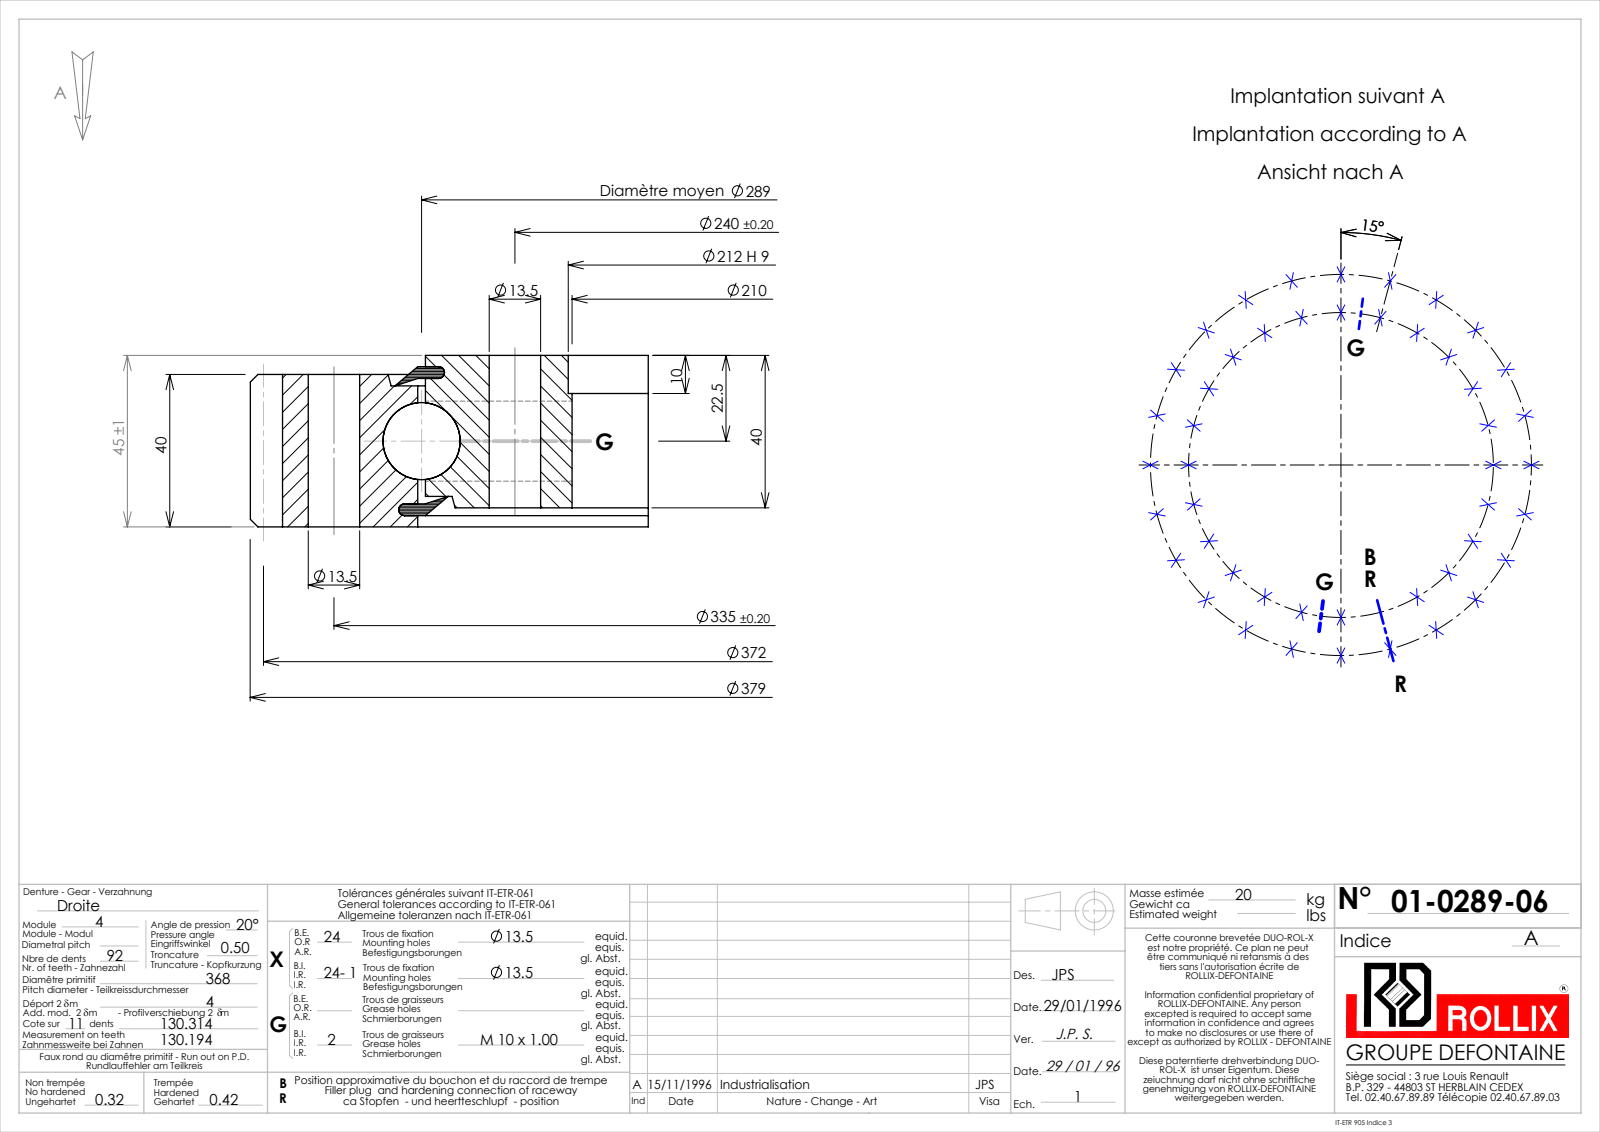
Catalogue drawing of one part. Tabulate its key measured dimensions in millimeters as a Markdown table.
| quantity | value |
| --- | --- |
| part name | 01-0289-06 |
| STEP written by | SolidWorks 2016 (CONFIG_CONTROL_DESIGN) |
| units | millimeters |
| bodies | 5 solids, 714 faces (199 planar, 299 cylindrical, 216 other) |
| overall size | 378.9 × 378.9 × 45 |
| volume | 2 328 000 mm³ |
| surface area | 487 615 mm² |
| round holes (diameter × count) | 13.5 × 47, 9 × 2, 210 × 1, 212 × 1, 291.02 × 1 |
| round bosses / shafts (diameter × count) | 286.98 × 1 |
| partial cylindrical surfaces (radius × count) | 181 × 1, 189.5 × 1 |
| main face-to-face distances | 40, 5, 45, 35, 6.05, 38.95, 1.05, 33.95, 2.95, 42.05 |
| hole center spacings | 167.5, 128.2, 203.93, 236.88, 265.77, 309.5, 332.13, 86.7 |
